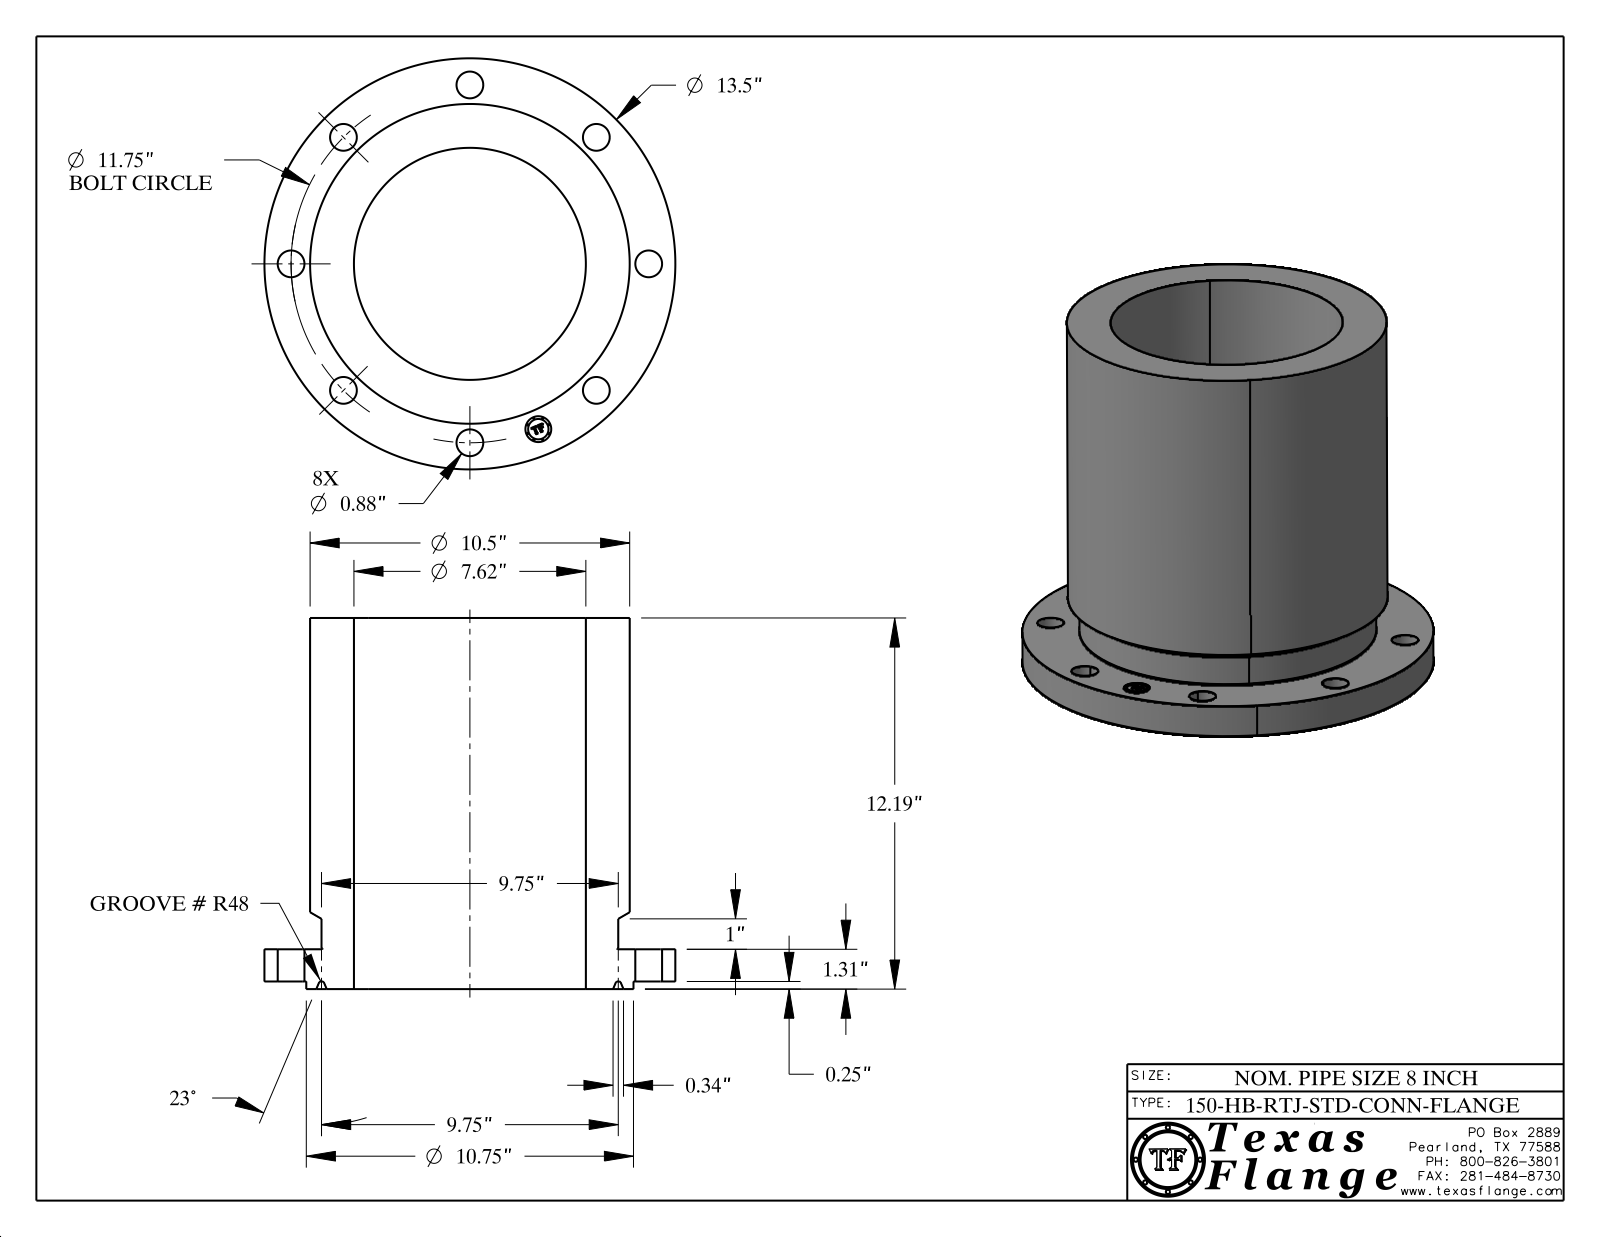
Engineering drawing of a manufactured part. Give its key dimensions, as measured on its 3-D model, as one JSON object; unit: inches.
{"part_name": "8-150-HB-RTJ-STD-CONN-FLANGE", "step_written_by": "CATIA V5 STEP AP214 (AUTOMOTIVE_DESIGN)", "units": "inches", "bodies": {"solids": 1, "faces": 431, "planar": 371, "cylindrical": 46, "other": 14}, "overall_size": [13.5, 13.5, 12.188], "volume_in3": 540.1, "surface_area_in2": 940, "round_holes": [[0.88, 8], [0.85, 1], [7.62, 1]], "round_bosses_or_shafts": [[0.051, 8], [13.5, 1], [10.75, 1], [10.5, 1], [9.75, 1], [0.67, 1]], "face_to_face_distances": [1.057, 11.937, 10.88, 0.25, 1.307, 12.187, 1.302, 1.052, 10.885, 0.254], "hole_center_spacings": [5.875, 4.496, 8.309, 10.856, 11.75, 9.77, 2.292, 2.293]}
